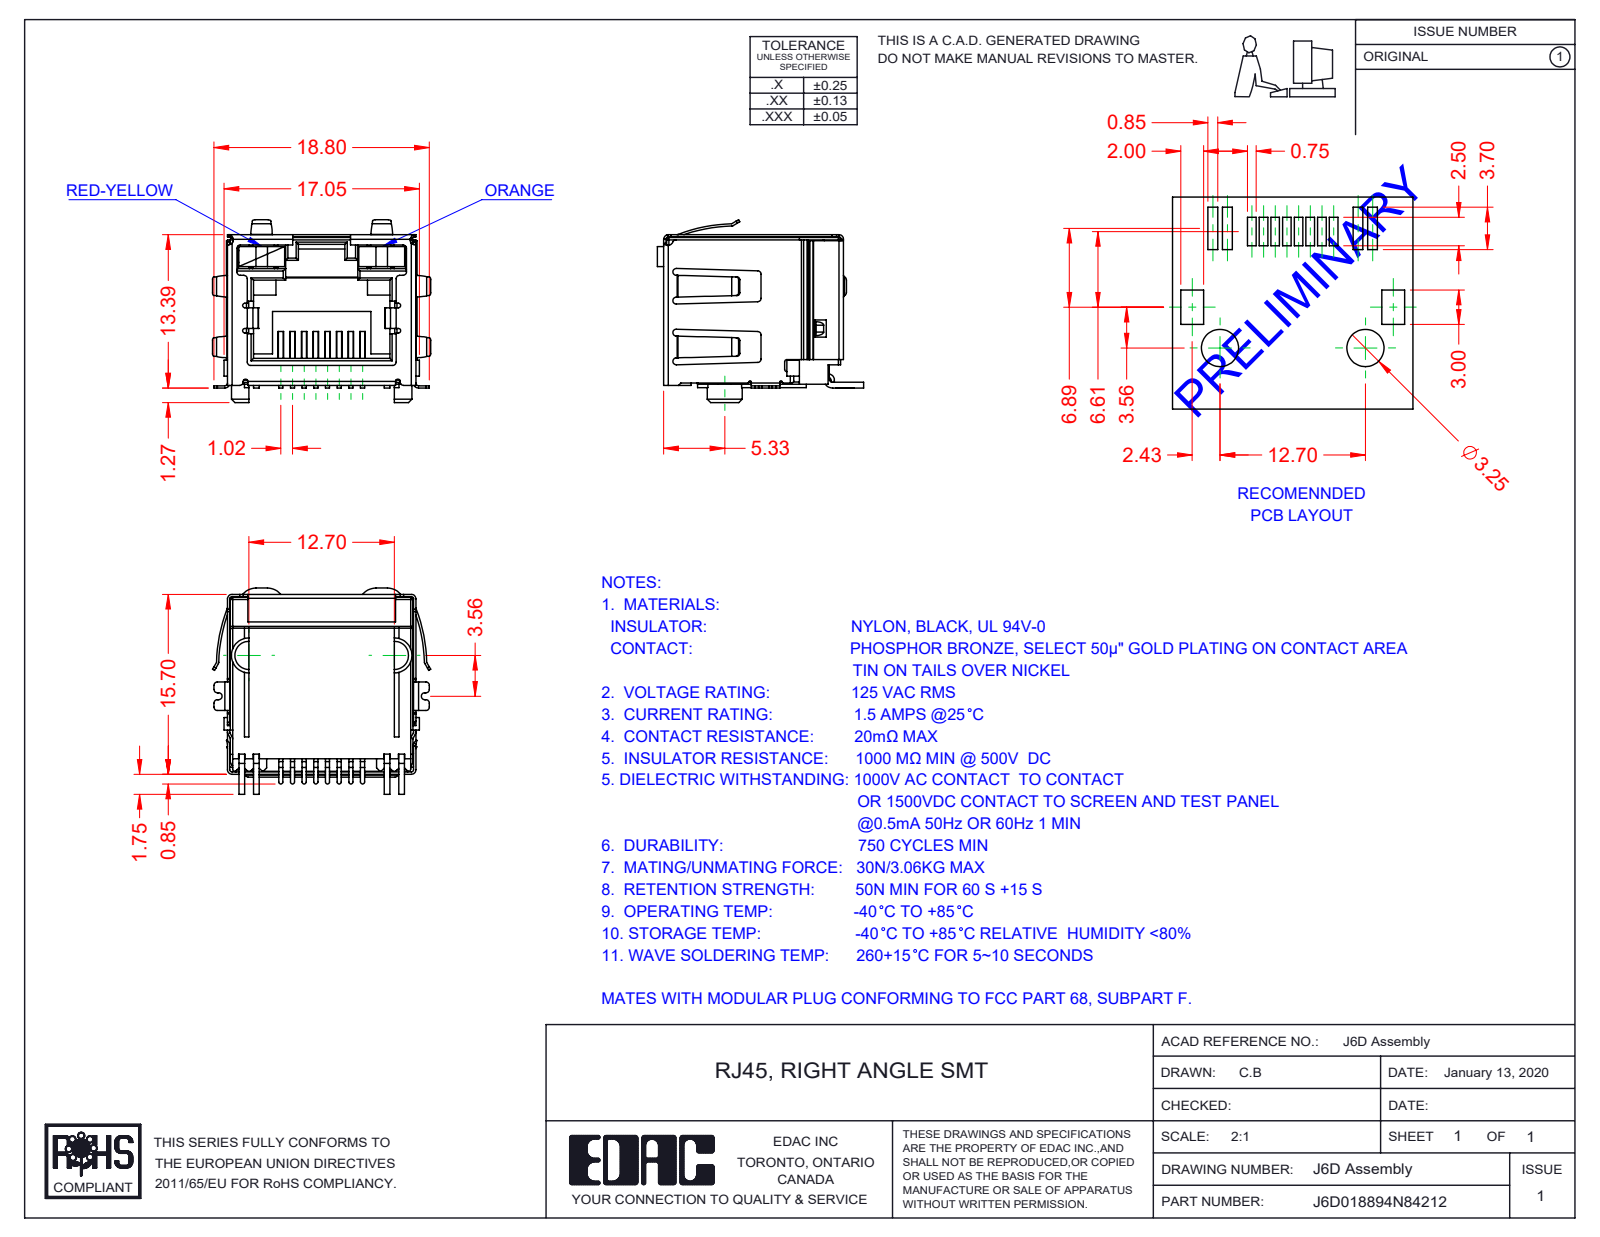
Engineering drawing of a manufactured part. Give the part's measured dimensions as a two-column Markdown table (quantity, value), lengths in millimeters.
| quantity | value |
| --- | --- |
| part name | 6D LED RH_4-Orange; 6D Contacts; 6D Insulator; 6D Shield_LED - EMI (+2 more) |
| STEP written by | SolidWorks 2016 (CONFIG_CONTROL_DESIGN) |
| units | millimeters |
| bodies | 12 solids, 1031 faces (702 planar, 284 cylindrical, 45 other) |
| overall size | 19.06 × 18 × 15.95 |
| volume | 1 790 mm³ |
| surface area | 4 796 mm² |
| partial cylindrical surfaces (radius × count) | 0.3 × 55, 0.2 × 40, 0.4 × 19, 0.25 × 16, 0.1 × 12, 0.15 × 8, 0.18 × 8, 0.5 × 6 |
| main face-to-face distances | 16, 16.2, 16.25, 2.25, 1, 15.95, 12.8, 0.45, 13.05, 10.6 |
